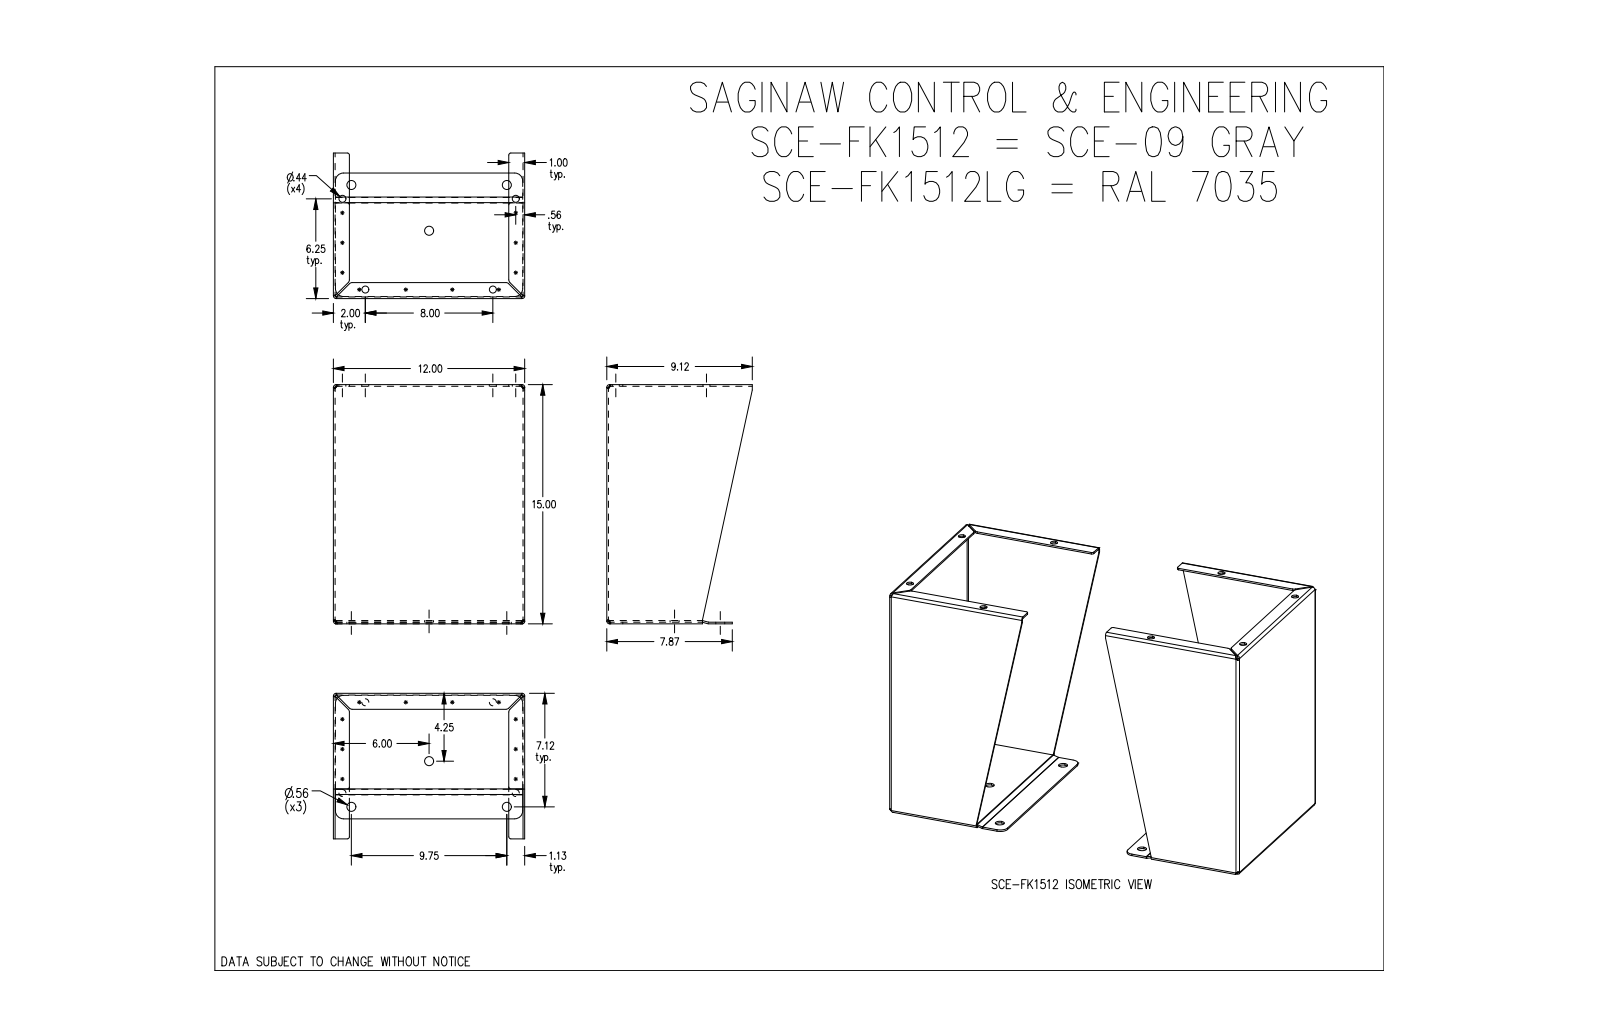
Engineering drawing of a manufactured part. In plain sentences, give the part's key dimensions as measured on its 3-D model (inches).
The part is named "SCE-FK1512". Its 3-D file was written by "SolidWorks 2019 (CONFIG_CONTROL_DESIGN)". It is 4 solids with 214 faces: 96 planar, 86 cylindrical and 32 other. Overall it measures 24 by 15 by 12 inches. Its volume is 110.9 cubic inches and its surface area 2 163 square inches. Round holes: 8 of diameter 0.437, 6 of diameter 0.563. Partial cylindrical surfaces (rounded edges, fillets, slot ends): 16 of radius 0.166, 12 of radius 0.062, 8 of radius 0.125, 8 of radius 0.22, 8 of radius 0.5, 4 of radius 0.063. The main face-to-face distances are 0.104, 11.896, 23.896, 12, 11.792, 23.792, 24, 14.792, 14.896, 0.101. The hole center spacings are 1.035, 5.441, 5.656, 5.793, 5.866, 6.614, 10.646, 11.019.
